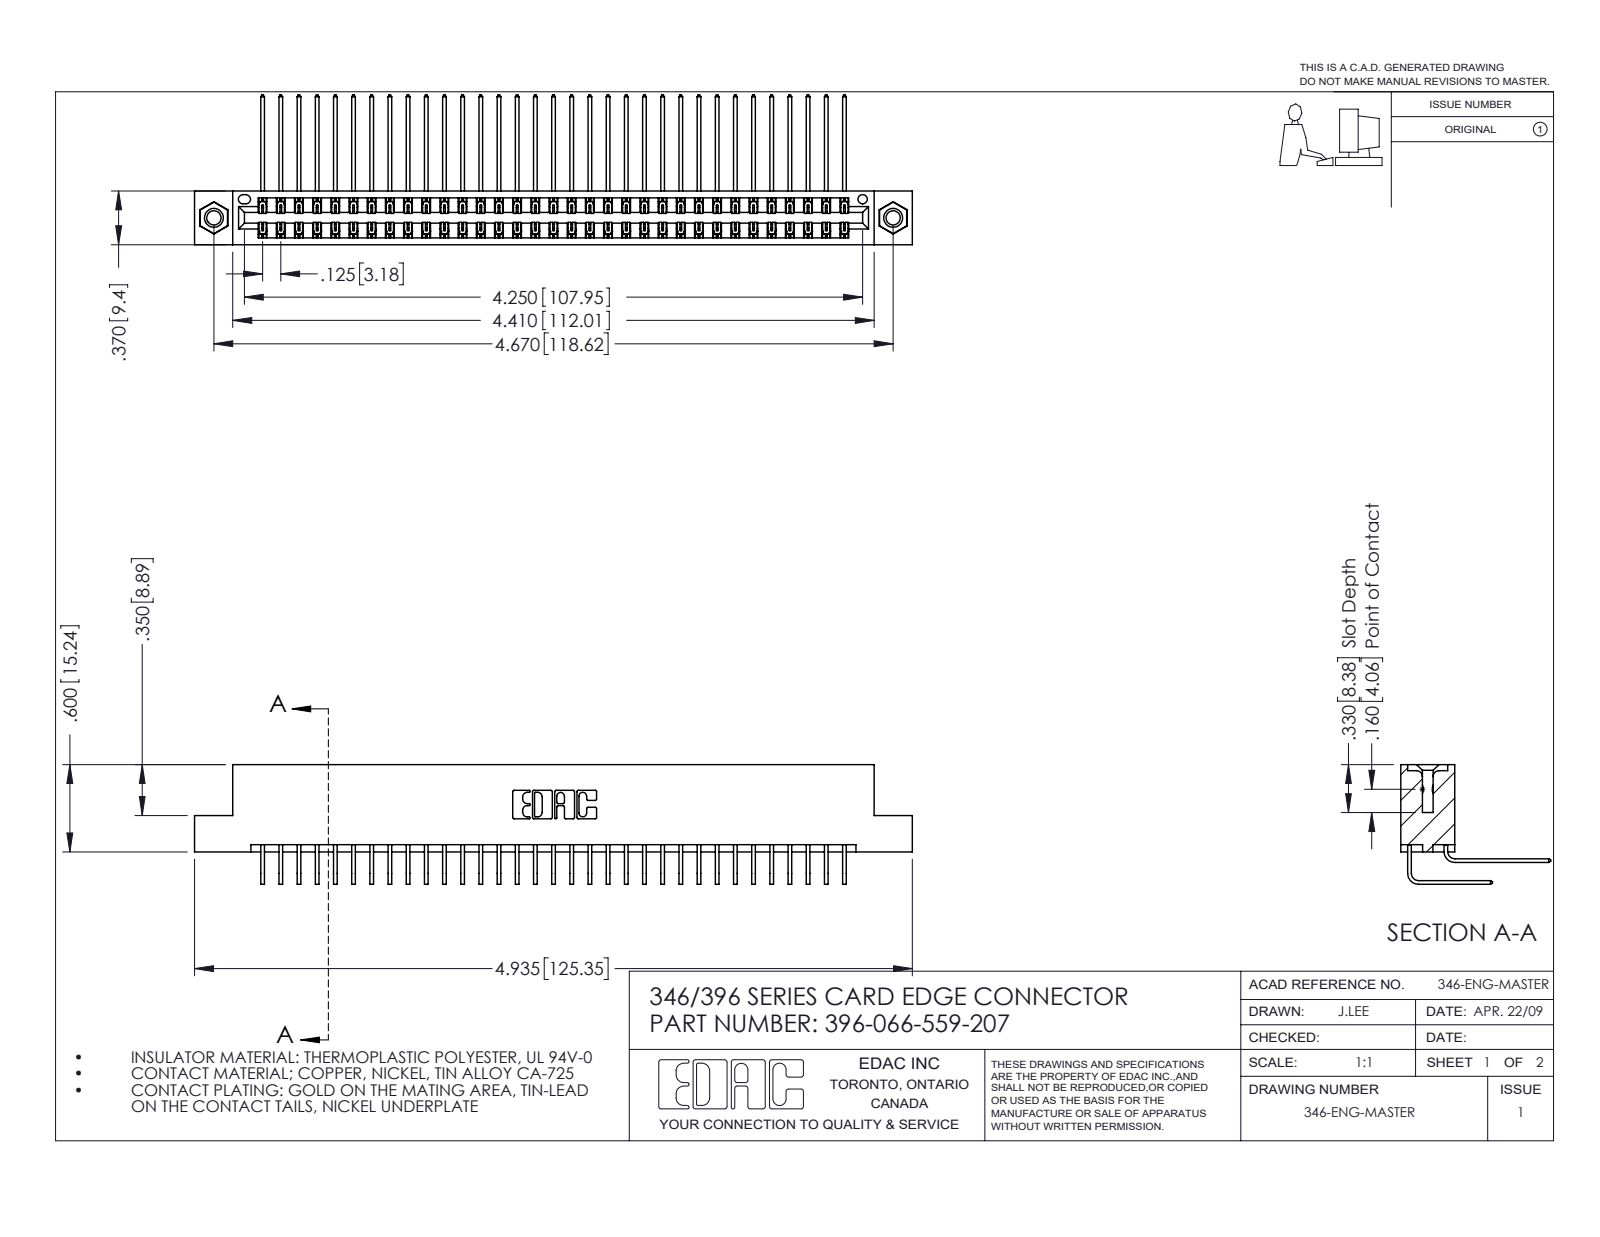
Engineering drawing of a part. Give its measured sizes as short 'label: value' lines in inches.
name: 396-066-559-207; 346 Part_Flush Mounting Lugs - 0.156 Dia-TI; 345-292-001_559 Tail - 2; 345-250-001_345-250-005-103 (+1 more)
written by: SolidWorks 2016 (CONFIG_CONTROL_DESIGN)
unit: in
bodies: 69 solids, 3746 faces (2550 planar, 1180 cylindrical, 16 other)
size: 4.935 × 1.03 × 0.823
volume: 0.764 in³; area: 29.34 in²
holes: 2× ⌀0.098, 2× ⌀0.125, 2× ⌀0.156, 1× ⌀0.064
bosses: 2× ⌀0.155
rounds: 99× R0.006, 22× R0.01, 6× R0.007, 6× R0.031, 3× R0.026, 2× R0.014, 2× R0.022, 2× R0.024
face distances: 0.048, 0.322, 0.025, 0.37, 0.25, 0.072, 0.298, 0.275, 0.148, 0.222
hole spacings: 0.246, 4.462, 4.67
